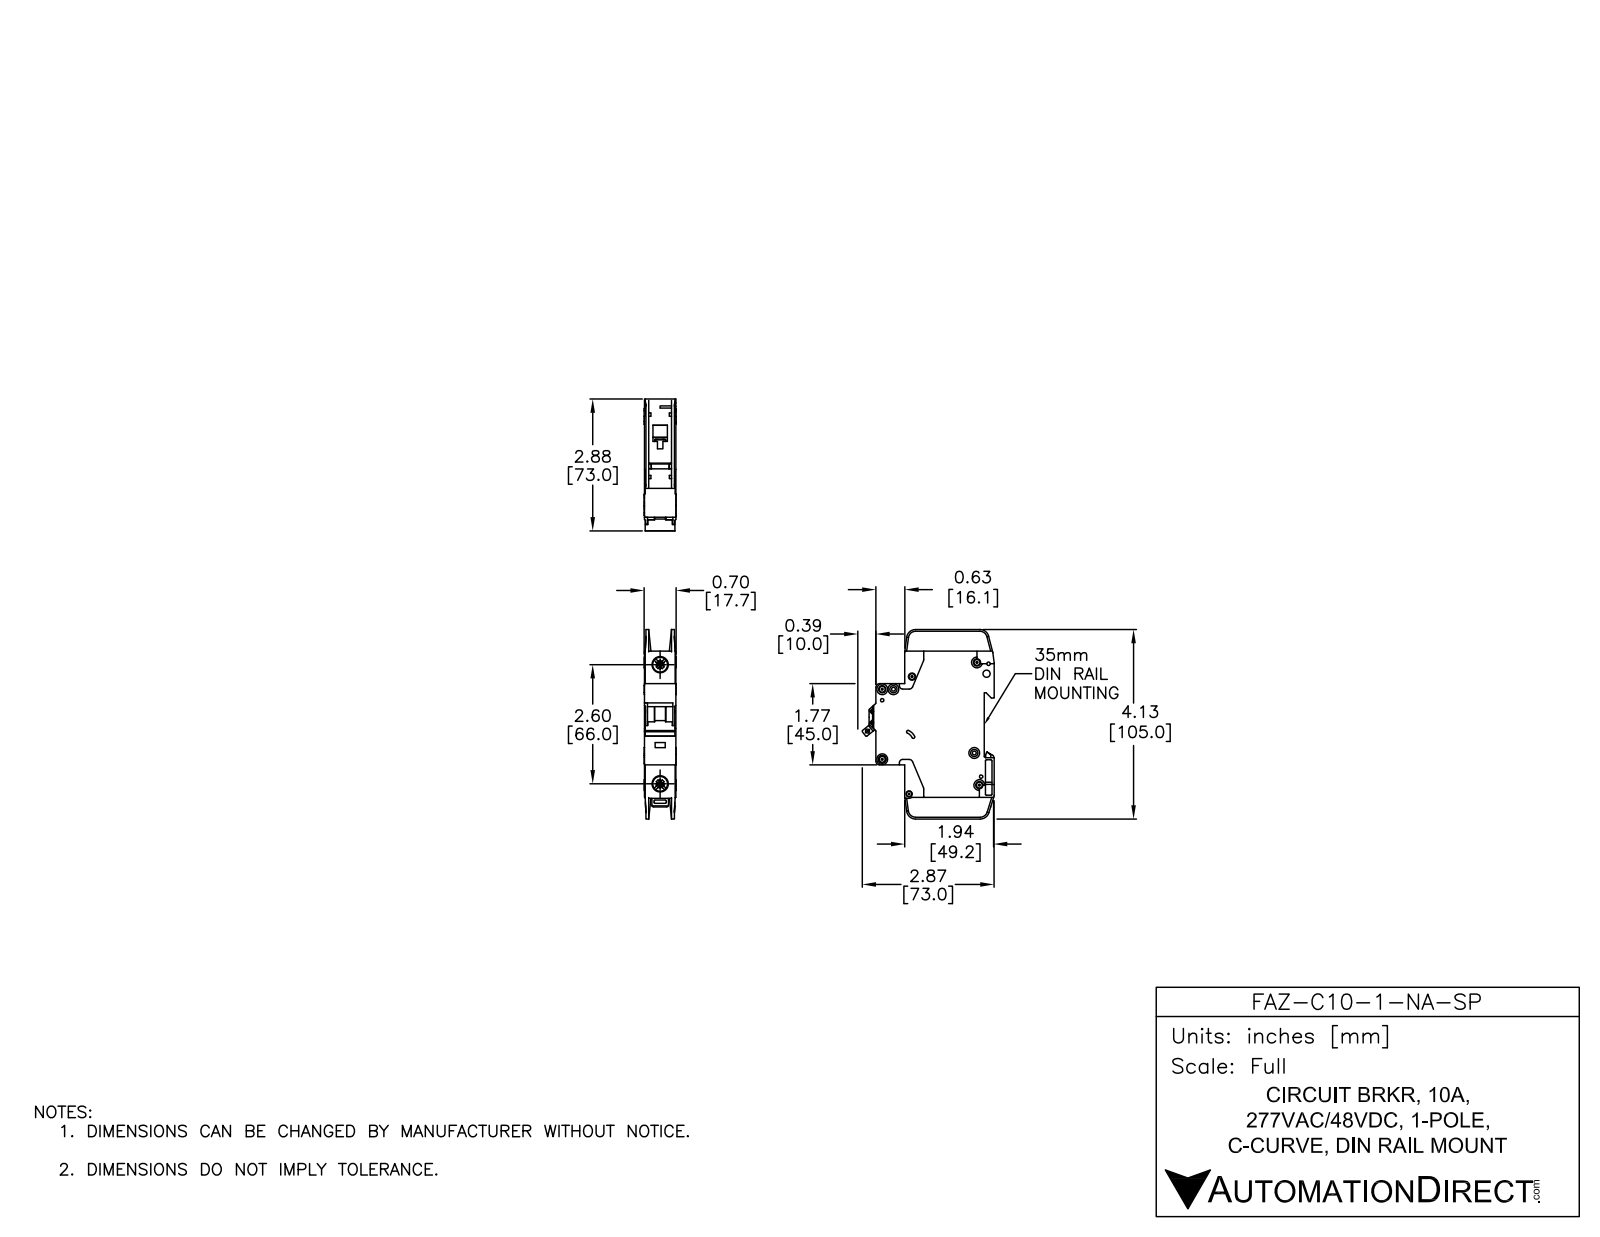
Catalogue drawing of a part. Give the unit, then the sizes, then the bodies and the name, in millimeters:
Units: millimetres
Overall size (bounding box): 105 × 73.04 × 17.7
Round holes (diameter × count): ⌀3.6 ×7, ⌀1.09 ×2, ⌀1.5 ×2, ⌀4 ×2, ⌀7.15 ×2, ⌀8.2 ×2, ⌀1.9 ×1, ⌀2.15 ×1, ⌀2.2 ×1, ⌀2.55 ×1, ⌀3.3 ×1, ⌀3.4 ×1
Round bosses / shafts (diameter × count): ⌀6 ×7, ⌀2.5 ×1
Partial cylindrical surfaces — rounded edges, fillets, slot ends (radius × count): R0.25 ×29, R0.5 ×18, R1 ×10, R2 ×10, R5 ×5, R4 ×4, R1.8 ×3, R0.2 ×2
Main face-to-face distances: 17.5, 15.05, 0.7, 2.45, 1.75, 15.75, 13.3, 14, 12.6, 2
Hole centre spacings: 6.2, 5.19, 6.1, 8.19, 8.56, 8.7, 11.11, 12.45
Volume: 77 695 mm³ · Surface area: 24 740 mm²
Bodies: 3 solids, 784 faces (409 planar, 263 cylindrical, 112 other)
Part name (STEP PRODUCT): FAZ-C10-1-NA-SP
STEP written by: SolidWorks 2014 (AUTOMOTIVE_DESIGN)
